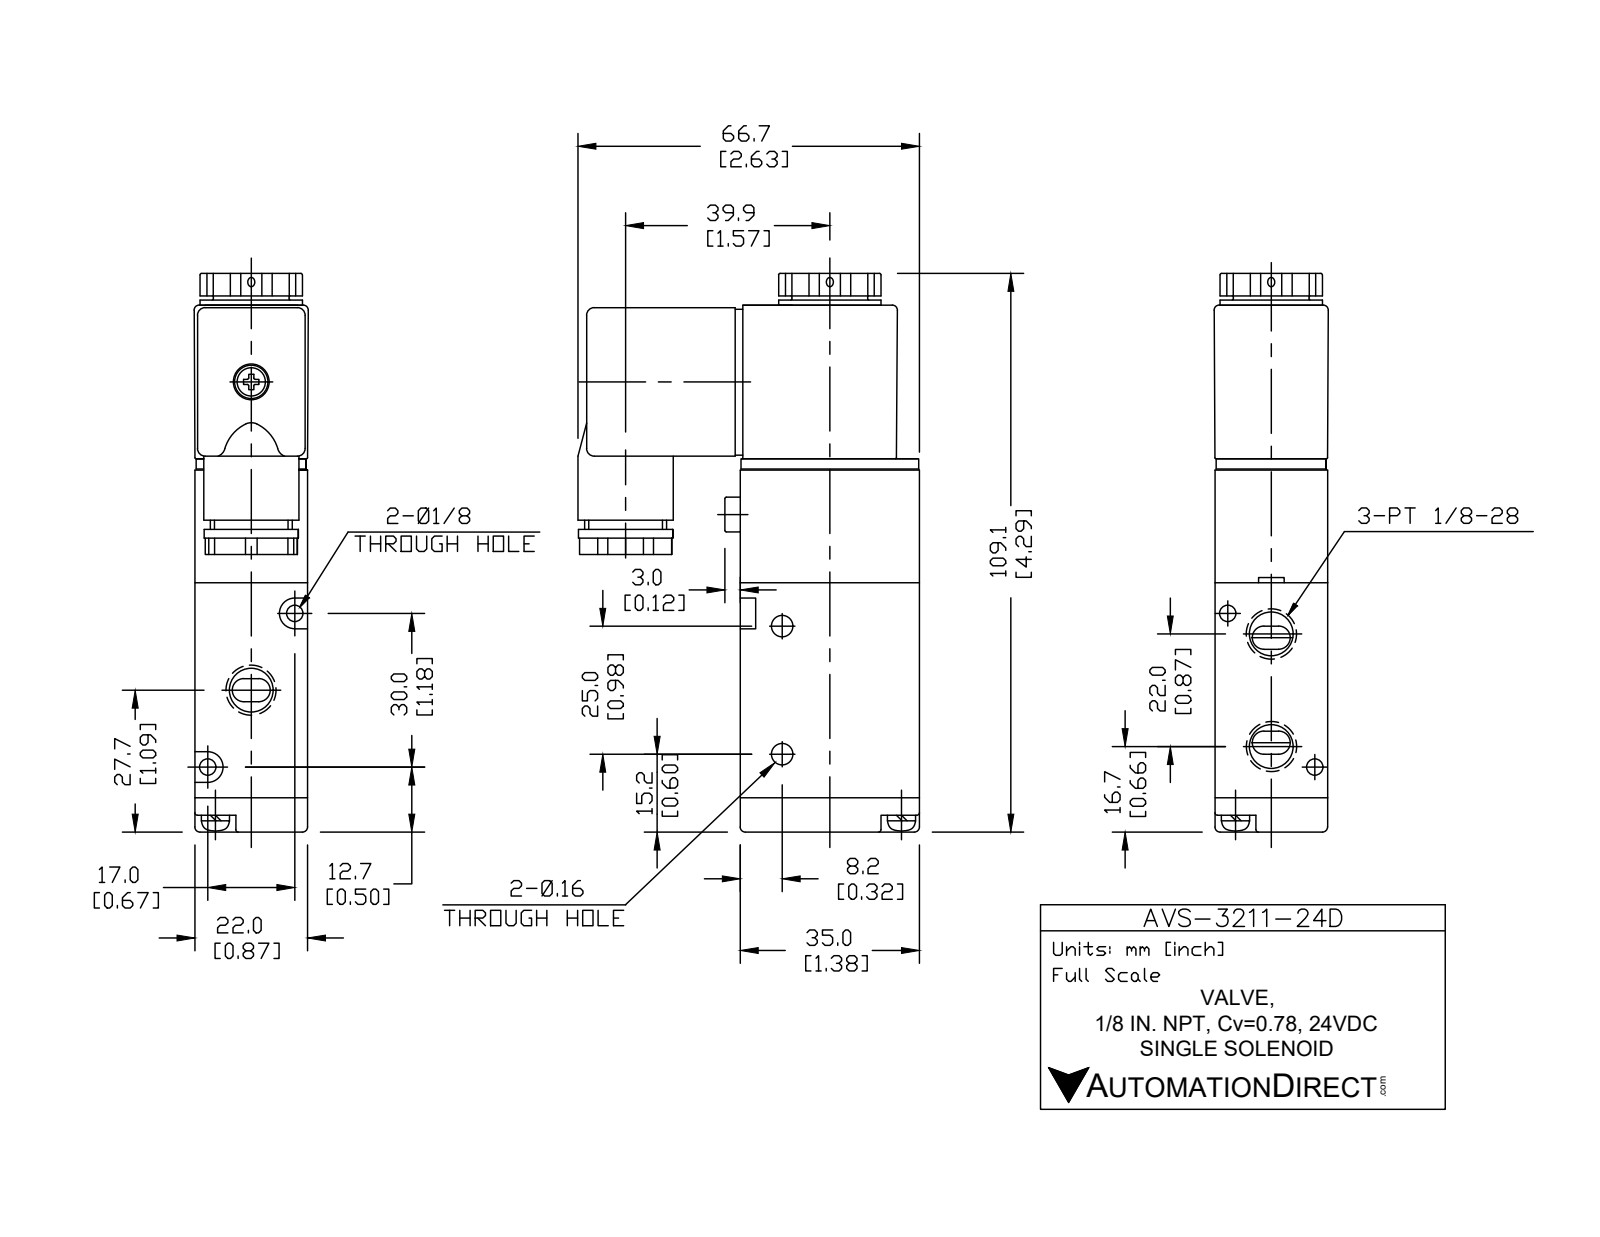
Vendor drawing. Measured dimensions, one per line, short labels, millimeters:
name: AVS-3211-24D
written by: SolidWorks 2015 (CONFIG_CONTROL_DESIGN)
unit: mm
bodies: 4 solids, 159 faces (84 planar, 53 cylindrical, 22 other)
size: 109.1 × 66.7 × 22
volume: 96 545 mm³; area: 23 276 mm²
holes: 3× ⌀8.43, 2× ⌀3.3, 2× ⌀4.3, 1× ⌀9.3
bosses: 1× ⌀20, 1× ⌀18.6, 1× ⌀18.4, 1× ⌀16, 1× ⌀14.8, 1× ⌀6.8
rounds: 11× R0.5, 10× R1, 2× R3
face distances: 0.5, 21.5, 42, 22, 6.7, 48.7, 21, 102.4, 35, 30
hole spacings: 9.39, 11, 17.24, 27.35, 22, 25, 34.48
